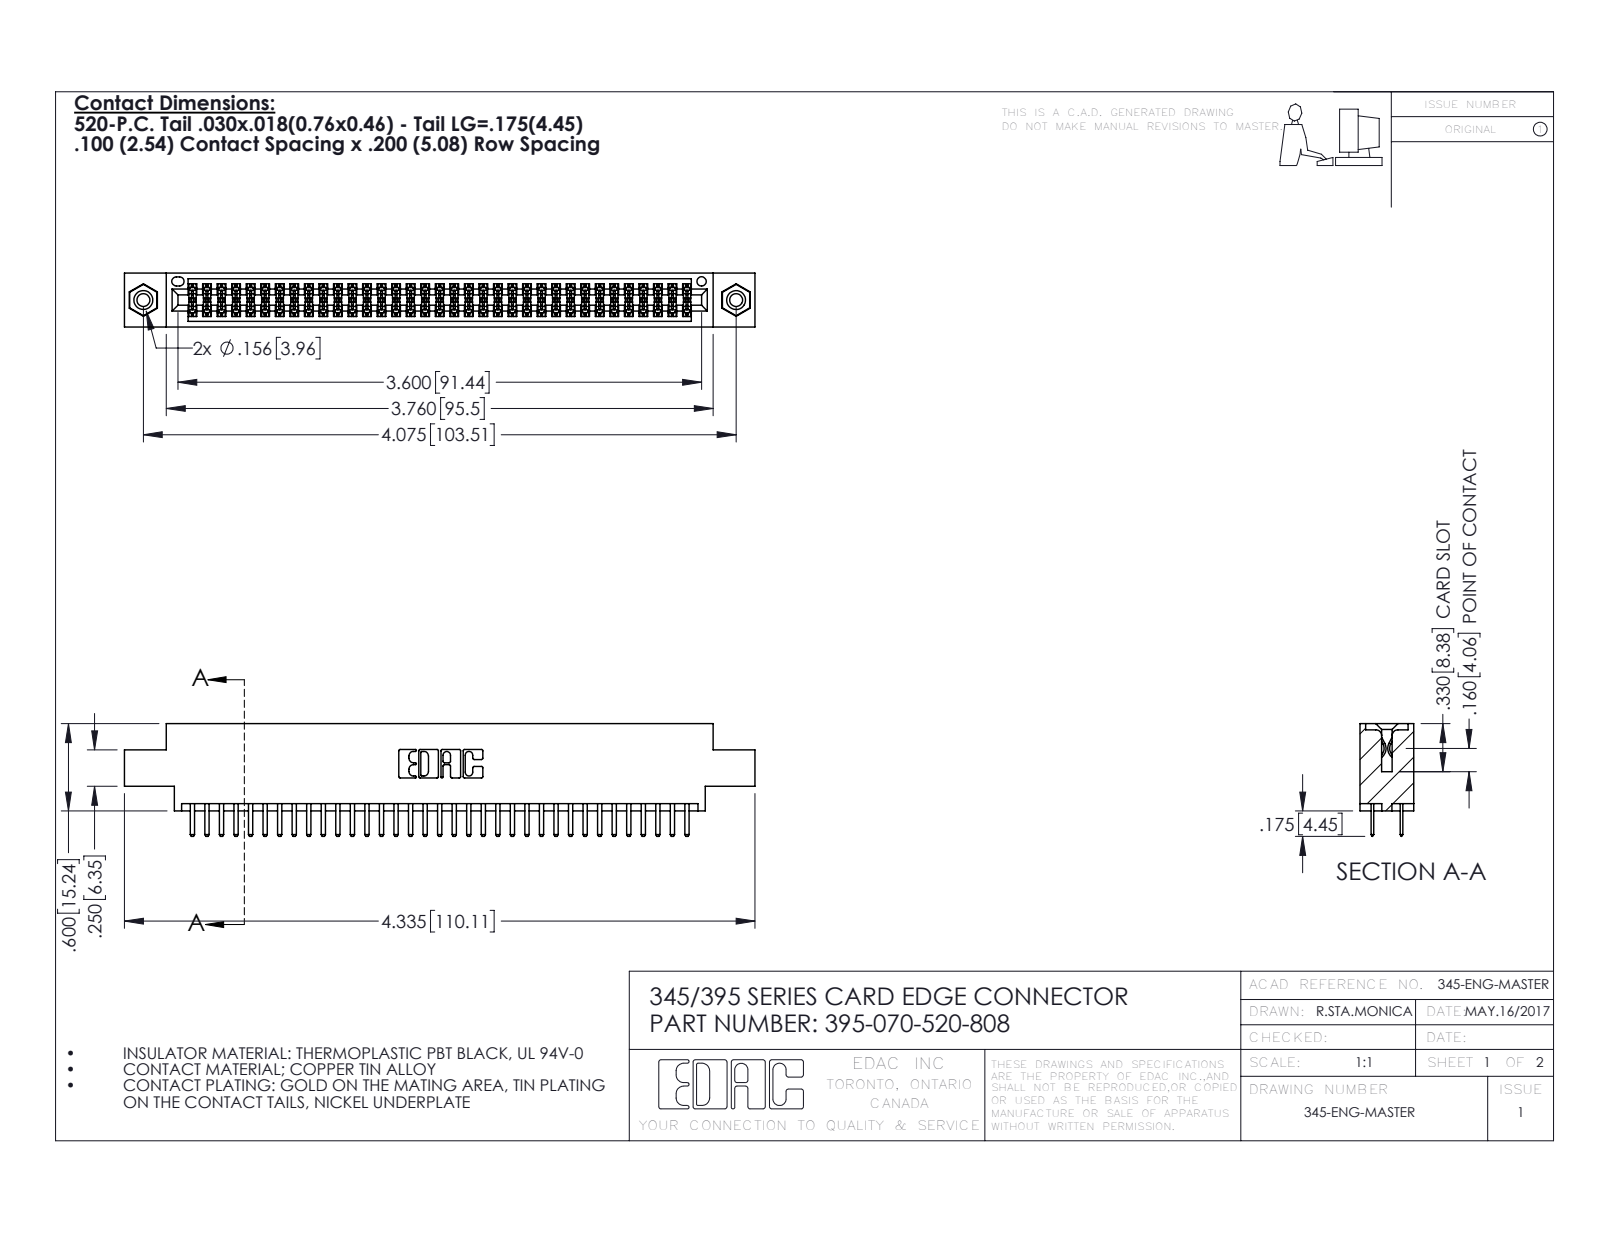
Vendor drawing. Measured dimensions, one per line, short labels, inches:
name: 345-292-001_345-293-120; 345 Part_0.170 Offset - 0.156 Dia-TI; 395-070-520-808; 345-250-001_345-250-003-102
written by: SolidWorks 2016 (CONFIG_CONTROL_DESIGN)
unit: in
bodies: 73 solids, 3970 faces (2566 planar, 1388 cylindrical, 16 other)
size: 4.335 × 0.775 × 0.37
volume: 0.64 in³; area: 23.94 in²
holes: 2× ⌀0.089, 2× ⌀0.125, 2× ⌀0.156, 1× ⌀0.064
bosses: 2× ⌀0.155
rounds: 105× R0.006, 74× R0.01, 22× R0.01, 6× R0.007, 6× R0.031, 3× R0.026, 2× R0.014, 2× R0.019
face distances: 0.072, 0.298, 0.2, 0.37, 0.098, 0.272, 0.025, 0.225, 0.022, 0.175
hole spacings: 0.27, 3.839, 4.075
